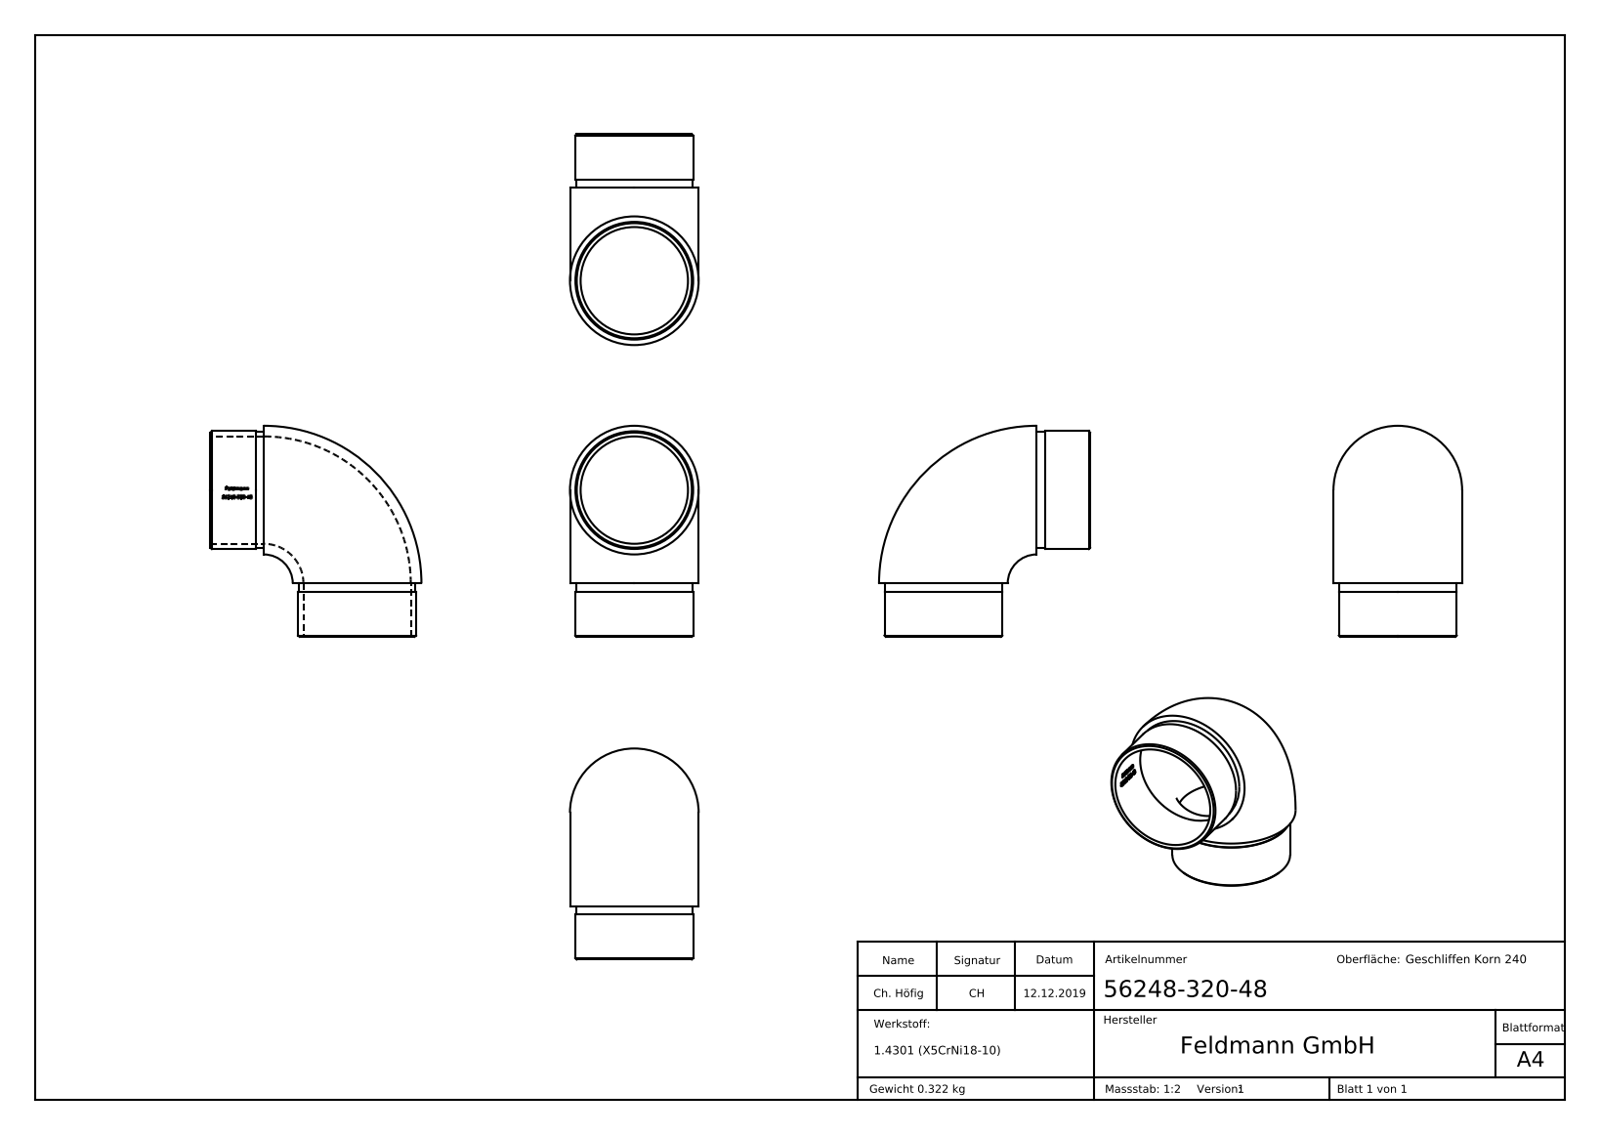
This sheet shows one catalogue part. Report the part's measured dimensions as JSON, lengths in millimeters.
{"part_name": "56248-320-48", "step_written_by": "SolidWorks 2015 (CONFIG_CONTROL_DESIGN)", "units": "millimeters", "bodies": {"solids": 1, "faces": 293, "planar": 118, "cylindrical": 37, "other": 138}, "overall_size": [79.2, 79.2, 48.3], "volume_mm3": 40799, "surface_area_mm2": 27135, "round_holes": [[40.3, 2]], "round_bosses_or_shafts": [[44.2, 2], [43.8, 2]], "partial_cylinders_radius": [[20.65, 1]], "face_to_face_distances": [20, 17, 3, 0.44, 0.39, 3.54, 2.97, 3.66, 3.27, 3.36]}
